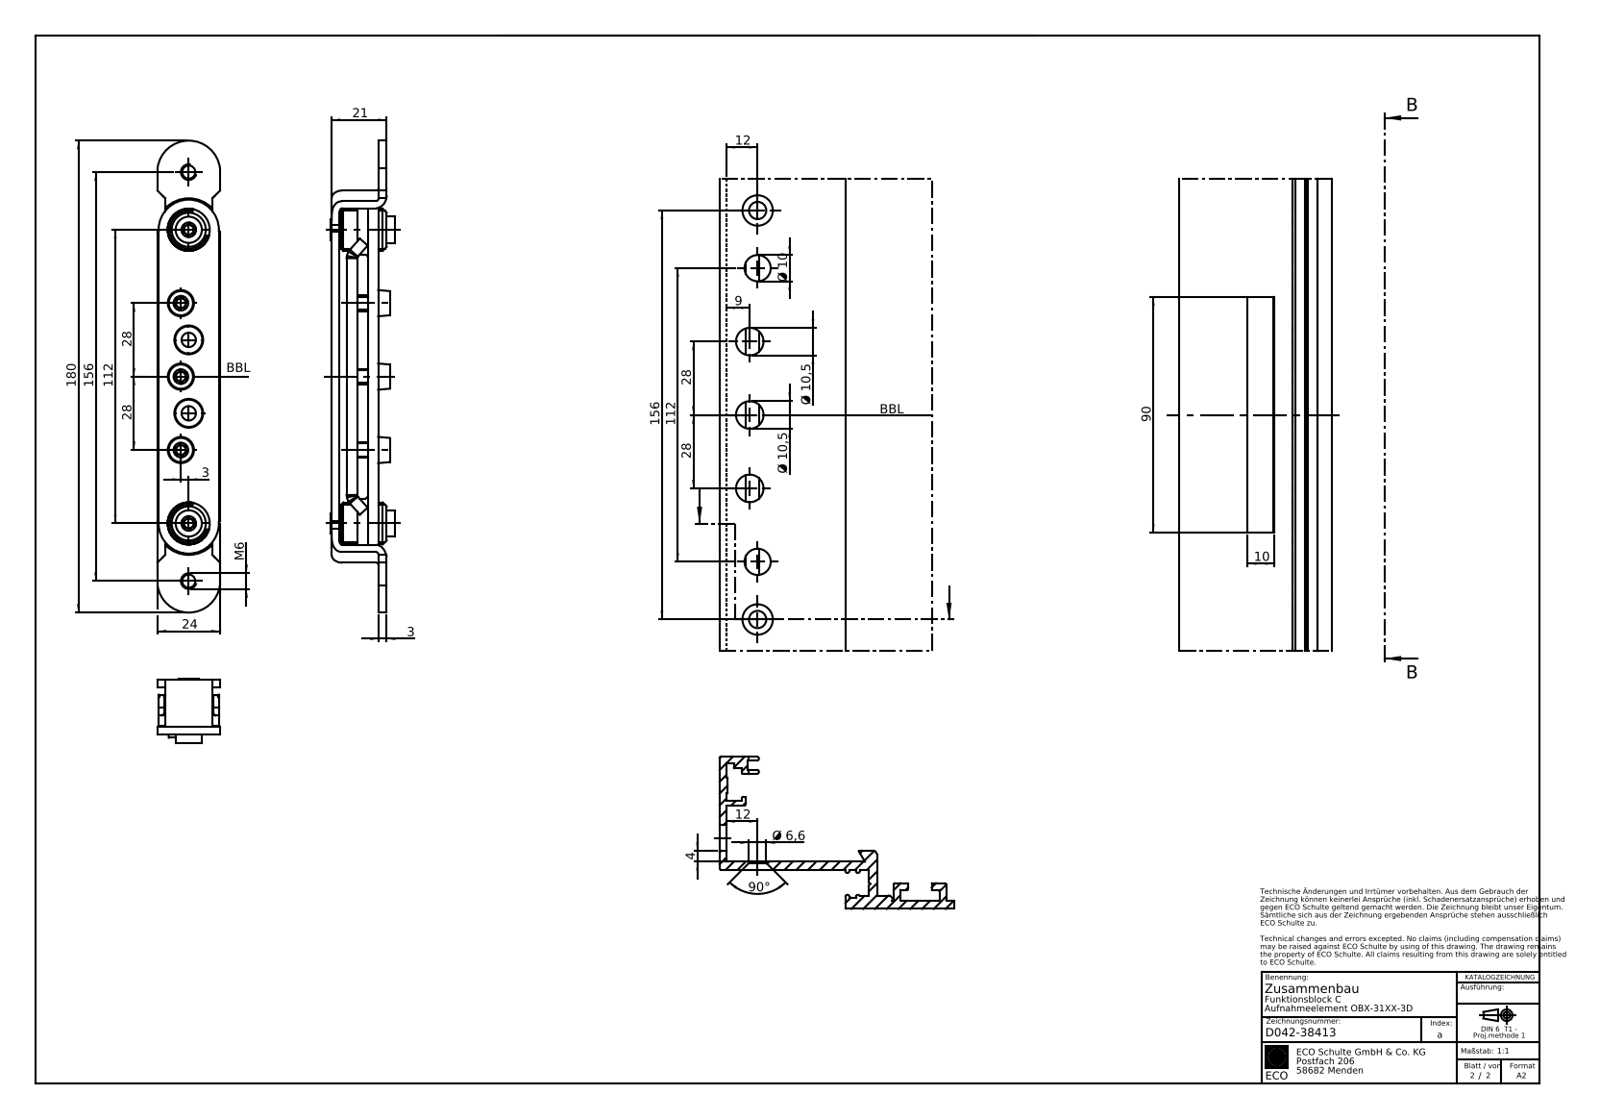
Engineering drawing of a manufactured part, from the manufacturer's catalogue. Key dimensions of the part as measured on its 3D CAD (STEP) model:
Part name (STEP PRODUCT): D042-28530_3mm-Mitte-Band; D043-38414_standard; D043-28535; D044-28536_verprgt (+3 more)
STEP written by: SolidWorks 2020 (AUTOMOTIVE_DESIGN)
Units: millimetres
Bodies: 8 solids, 362 faces (159 planar, 105 cylindrical, 98 other)
Overall size (bounding box): 180 × 24.25 × 23.8
Volume: 39 627 mm³ · Surface area: 27 915 mm²
Round holes (diameter × count): ⌀5 ×5, ⌀5.6 ×5, ⌀11 ×4, ⌀6.5 ×3, ⌀5.5 ×2, ⌀8.2 ×2, ⌀14.5 ×2
Round bosses / shafts (diameter × count): ⌀6 ×3, ⌀19 ×2, ⌀16 ×2, ⌀10 ×2, ⌀8.6 ×2, ⌀8 ×2
Partial cylindrical surfaces — rounded edges, fillets, slot ends (radius × count): R3 ×4, R12 ×4, R3.25 ×3, R1 ×2, R5 ×2, R11.5 ×2, R12.5 ×2
Main face-to-face distances: 4, 8, 3, 17.5, 14.5, 2.5, 6.5, 9.5, 13.5, 10.5
Hole centre spacings: 14.32, 28, 22, 28.16, 42, 42.11, 50.09, 56.08
